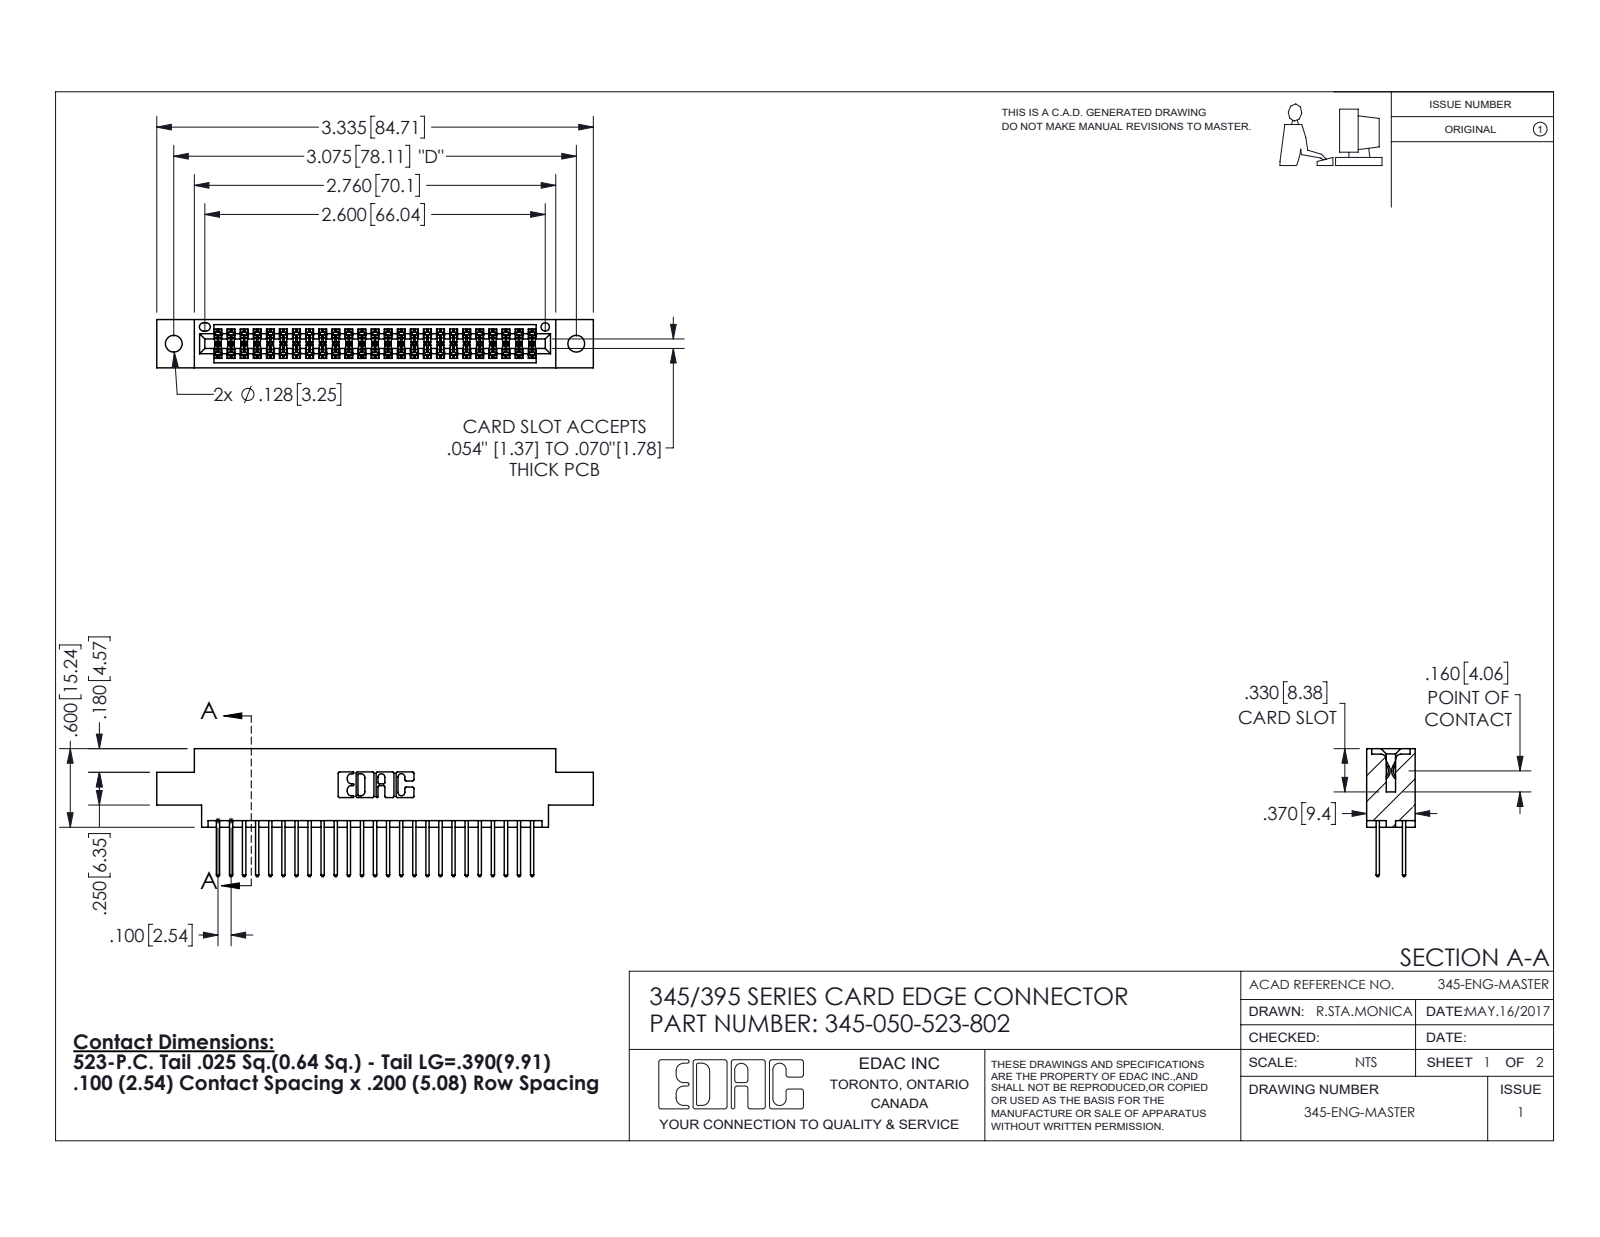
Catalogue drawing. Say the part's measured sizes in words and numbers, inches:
The part is named "345-292-001_345-293-123; 345-050-523-802; 345 Part_0.170 Offset - 0.128 Dia". Its 3-D file was written by "SolidWorks 2016 (CONFIG_CONTROL_DESIGN)". It is 51 solids with 2630 faces: 1734 planar, 896 cylindrical and 0 other. Overall it measures 3.335 by 0.977 by 0.37 inches. Its volume is 0.49 cubic inches and its surface area 18.38 square inches. Round holes: 2 of diameter 0.128, 1 of diameter 0.064. Partial cylindrical surfaces (rounded edges, fillets, slot ends): 75 of radius 0.006, 50 of radius 0.01, 22 of radius 0.01, 6 of radius 0.007, 6 of radius 0.031, 3 of radius 0.026, 2 of radius 0.014, 2 of radius 0.019. The main face-to-face distances are 0.298, 0.072, 0.2, 0.098, 0.272, 0.025, 0.37, 0.225, 0.175, 0.149. The hole center spacings are 0.27, 2.84, 3.075.
